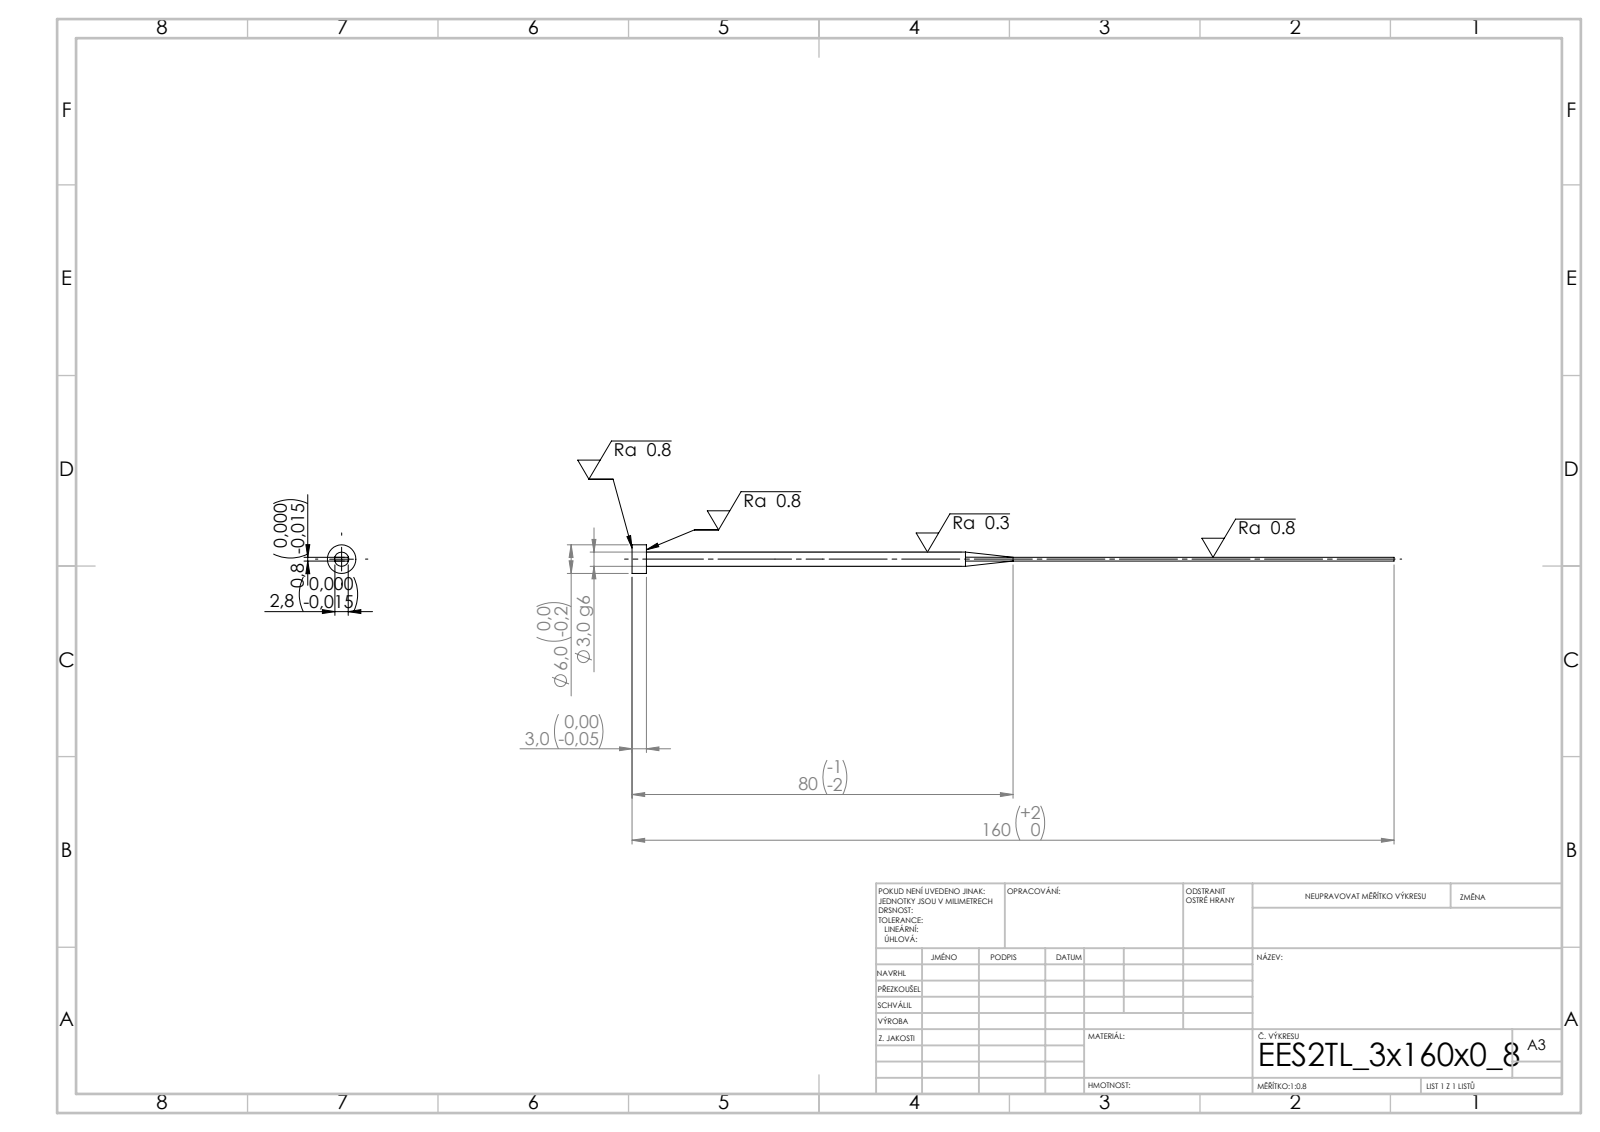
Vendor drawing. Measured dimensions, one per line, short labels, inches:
written by: SolidWorks 2019 (CONFIG_CONTROL_DESIGN)
unit: in
bodies: 1 solid, 15 faces (7 planar, 4 cylindrical, 4 other)
size: 6.299 × 0.236 × 0.236
volume: 0.048 in³; area: 2.164 in²
bosses: 1× ⌀0.236, 1× ⌀0.118
face distances: 0.031, 0.11, 0.118, 6.299, 6.181
